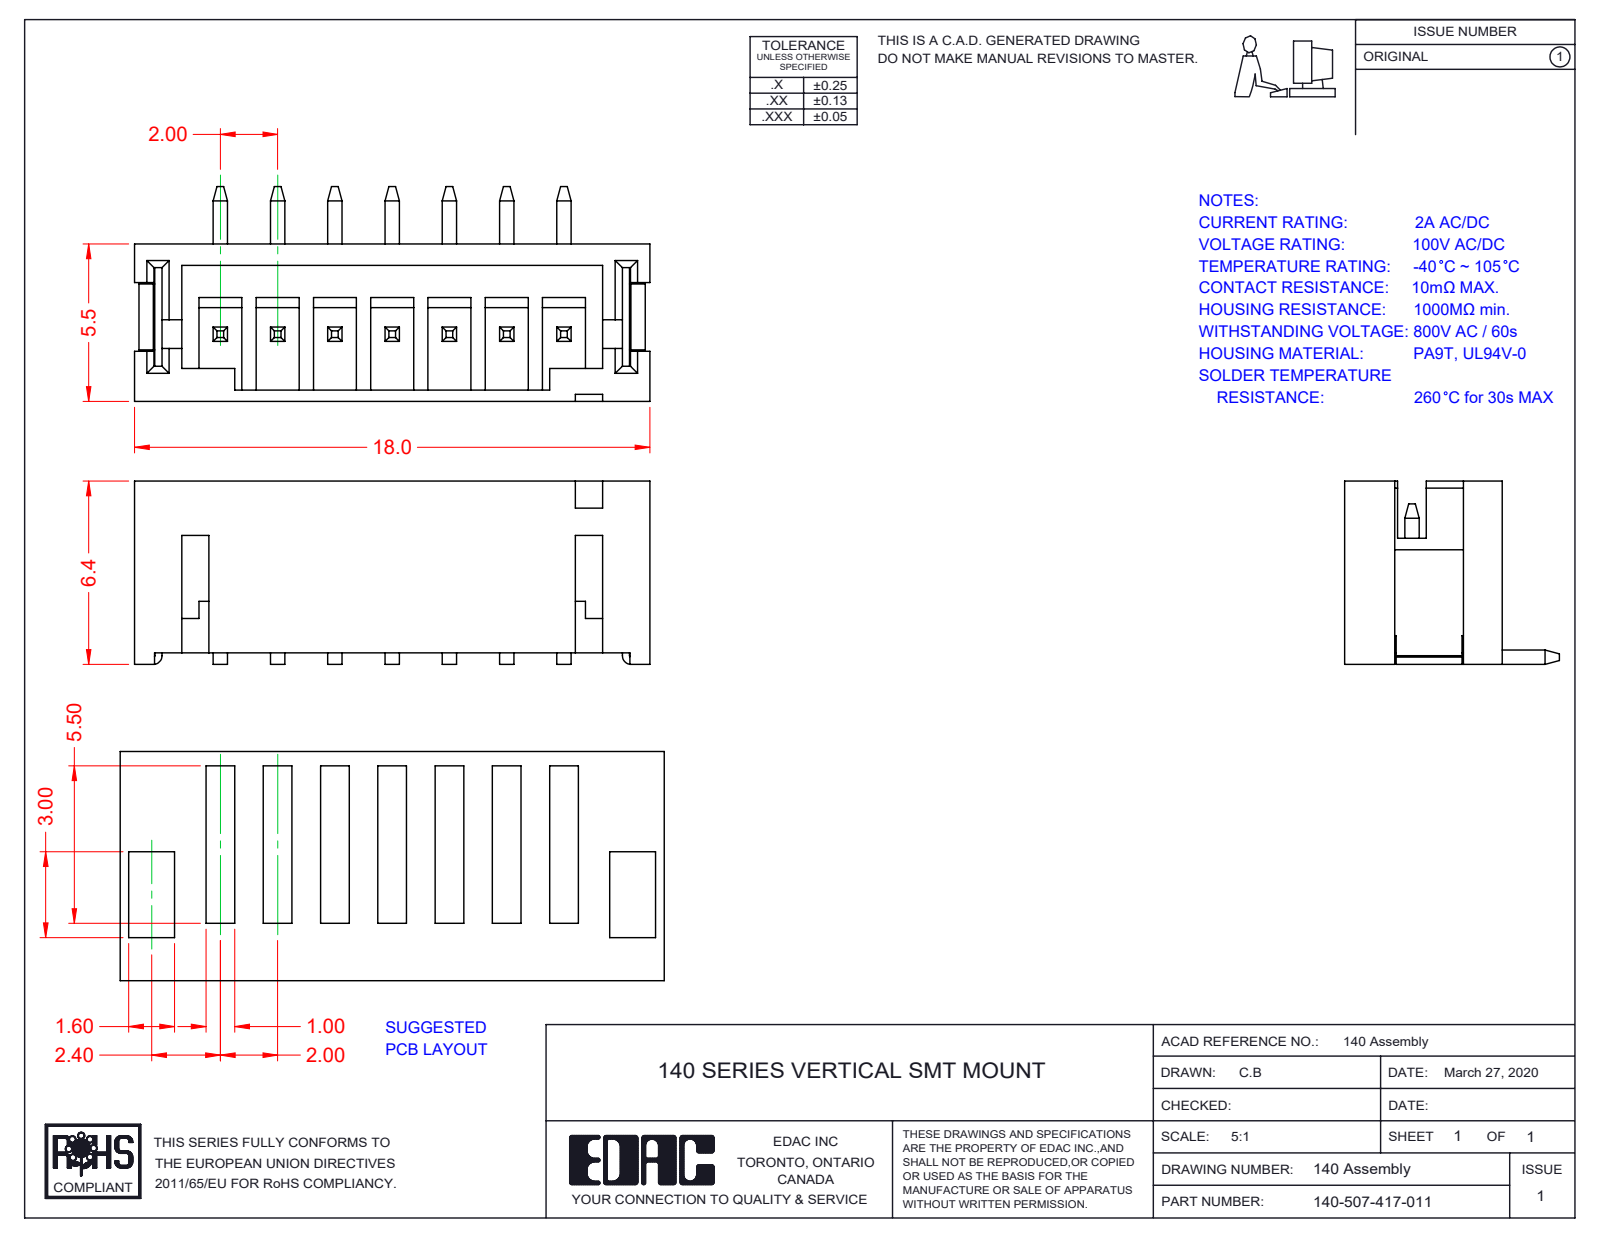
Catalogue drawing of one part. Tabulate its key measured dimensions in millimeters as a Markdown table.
| quantity | value |
| --- | --- |
| part name | V SMT Contact; 140-507-417-011; V SMT Pad; V SMT Housing_507 |
| STEP written by | SolidWorks 2016 (CONFIG_CONTROL_DESIGN) |
| units | millimeters |
| bodies | 10 solids, 366 faces (348 planar, 18 cylindrical, 0 other) |
| overall size | 18 × 7.5 × 6.4 |
| volume | 274 mm³ |
| surface area | 985 mm² |
| partial cylindrical surfaces (radius × count) | 0.3 × 2, 0.55 × 1 |
| main face-to-face distances | 5.5, 0.75, 4.75, 0.5, 0.4, 4.35, 5.1, 0.6, 6, 2 |
